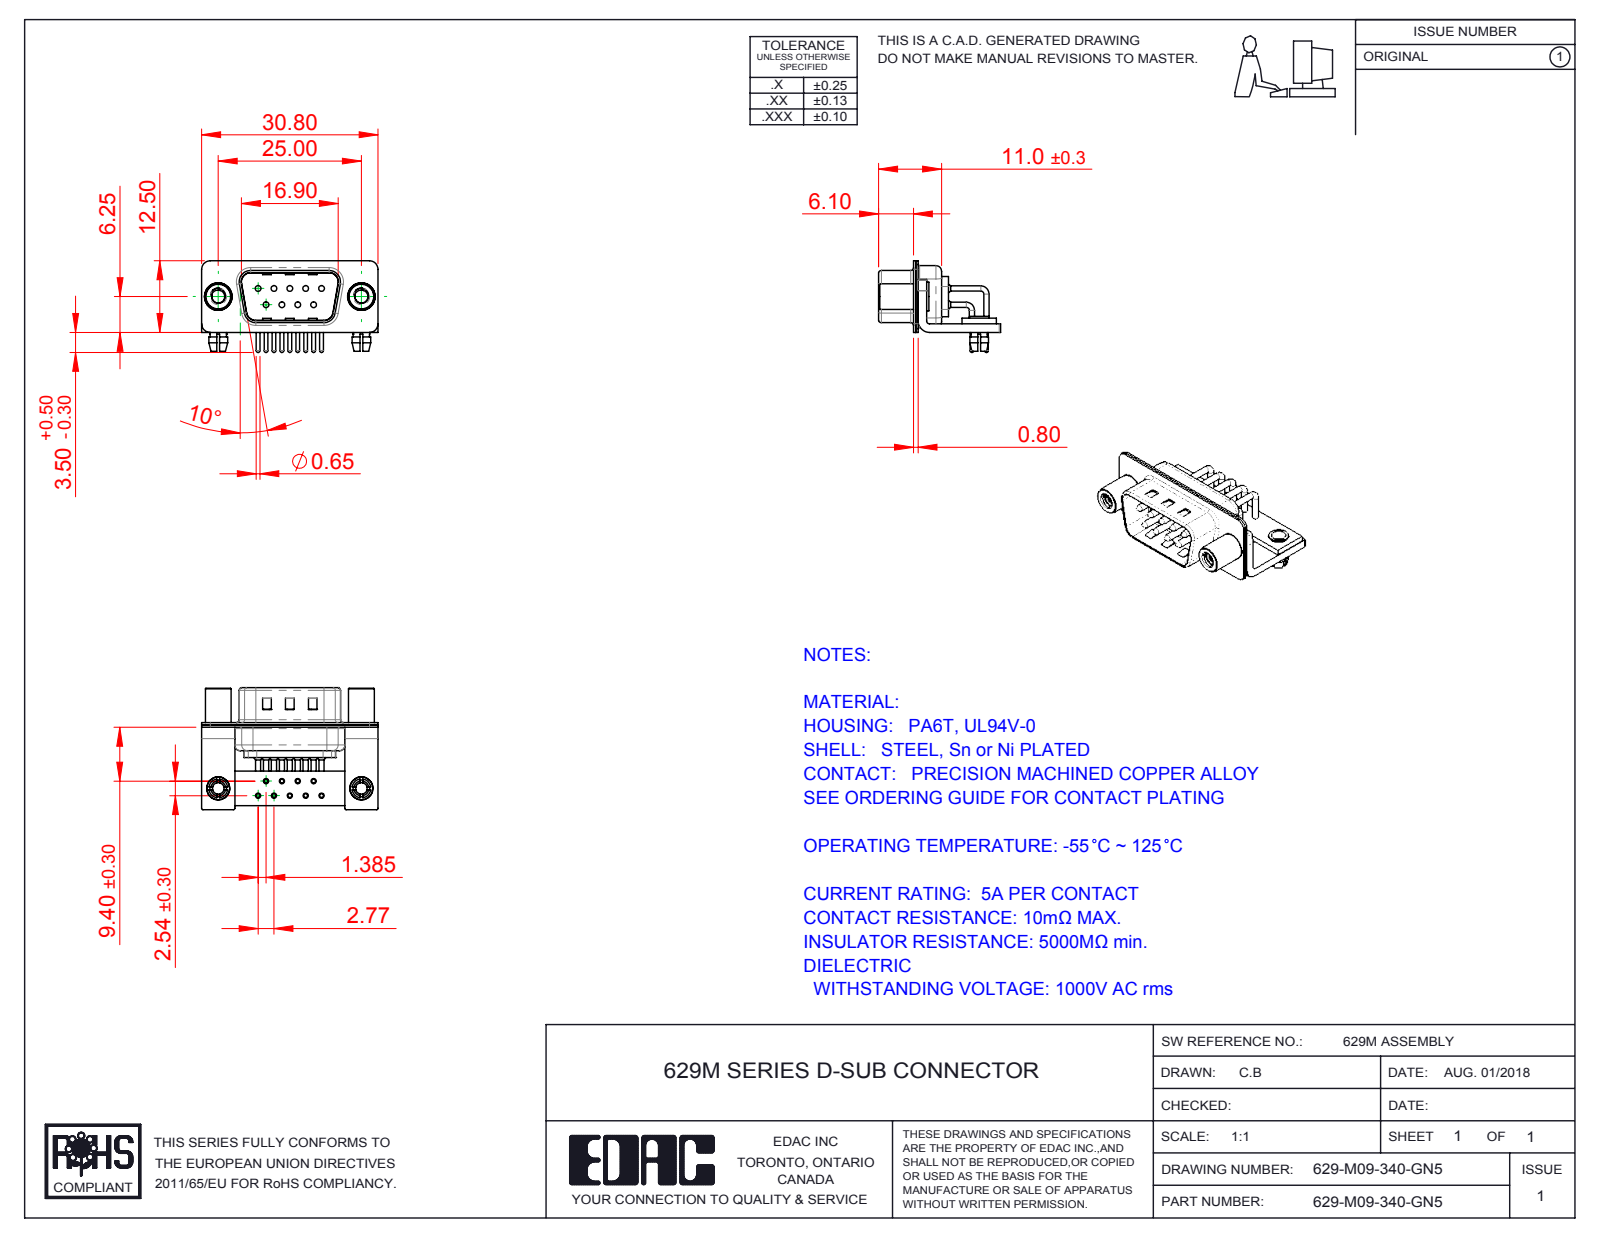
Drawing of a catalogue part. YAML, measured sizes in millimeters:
part_name: "629M Housing_09 Contacts; 629M Stabilizer Board_09 Contacts; 629M 4-40 Threaded Standoff; 629M Stabilizer Bracket (+6 more)"
step_written_by: "SolidWorks 2016 (CONFIG_CONTROL_DESIGN)"
units: millimeters
bodies: {solids: 19, faces: 1504, planar: 759, cylindrical: 567, other: 178}
overall_size: [30.8, 21.3, 16]
volume: 1984
surface_area: 5510
round_holes:
  - {diameter: 2, count: 11}
  - {diameter: 0.9, count: 9}
  - {diameter: 1, count: 9}
  - {diameter: 1.7, count: 9}
  - {diameter: 2.26, count: 2}
  - {diameter: 2.5, count: 2}
  - {diameter: 3.2, count: 2}
  - {diameter: 4, count: 2}
  - {diameter: 4.8, count: 2}
round_bosses_or_shafts:
  - {diameter: 1.5, count: 9}
  - {diameter: 0.9, count: 9}
  - {diameter: 0.65, count: 9}
  - {diameter: 5, count: 2}
  - {diameter: 4.9, count: 2}
  - {diameter: 4.5, count: 2}
  - {diameter: 4, count: 2}
  - {diameter: 3.4, count: 2}
partial_cylinders:
  - {radius: 0.25, count: 16}
  - {radius: 1.5, count: 16}
  - {radius: 2, count: 13}
  - {radius: 0.5, count: 9}
  - {radius: 1.01, count: 9}
  - {radius: 1.6, count: 8}
  - {radius: 0.6, count: 4}
  - {radius: 0.65, count: 4}
face_to_face_distances: [0.4, 1.5, 0.8, 0.85, 1.25, 1.9, 1, 2.5, 10.4, 9.55]
hole_center_spacings: [2.77, 5.54, 3.16, 4.87, 8.31, 2.89, 2.9, 5.03]
